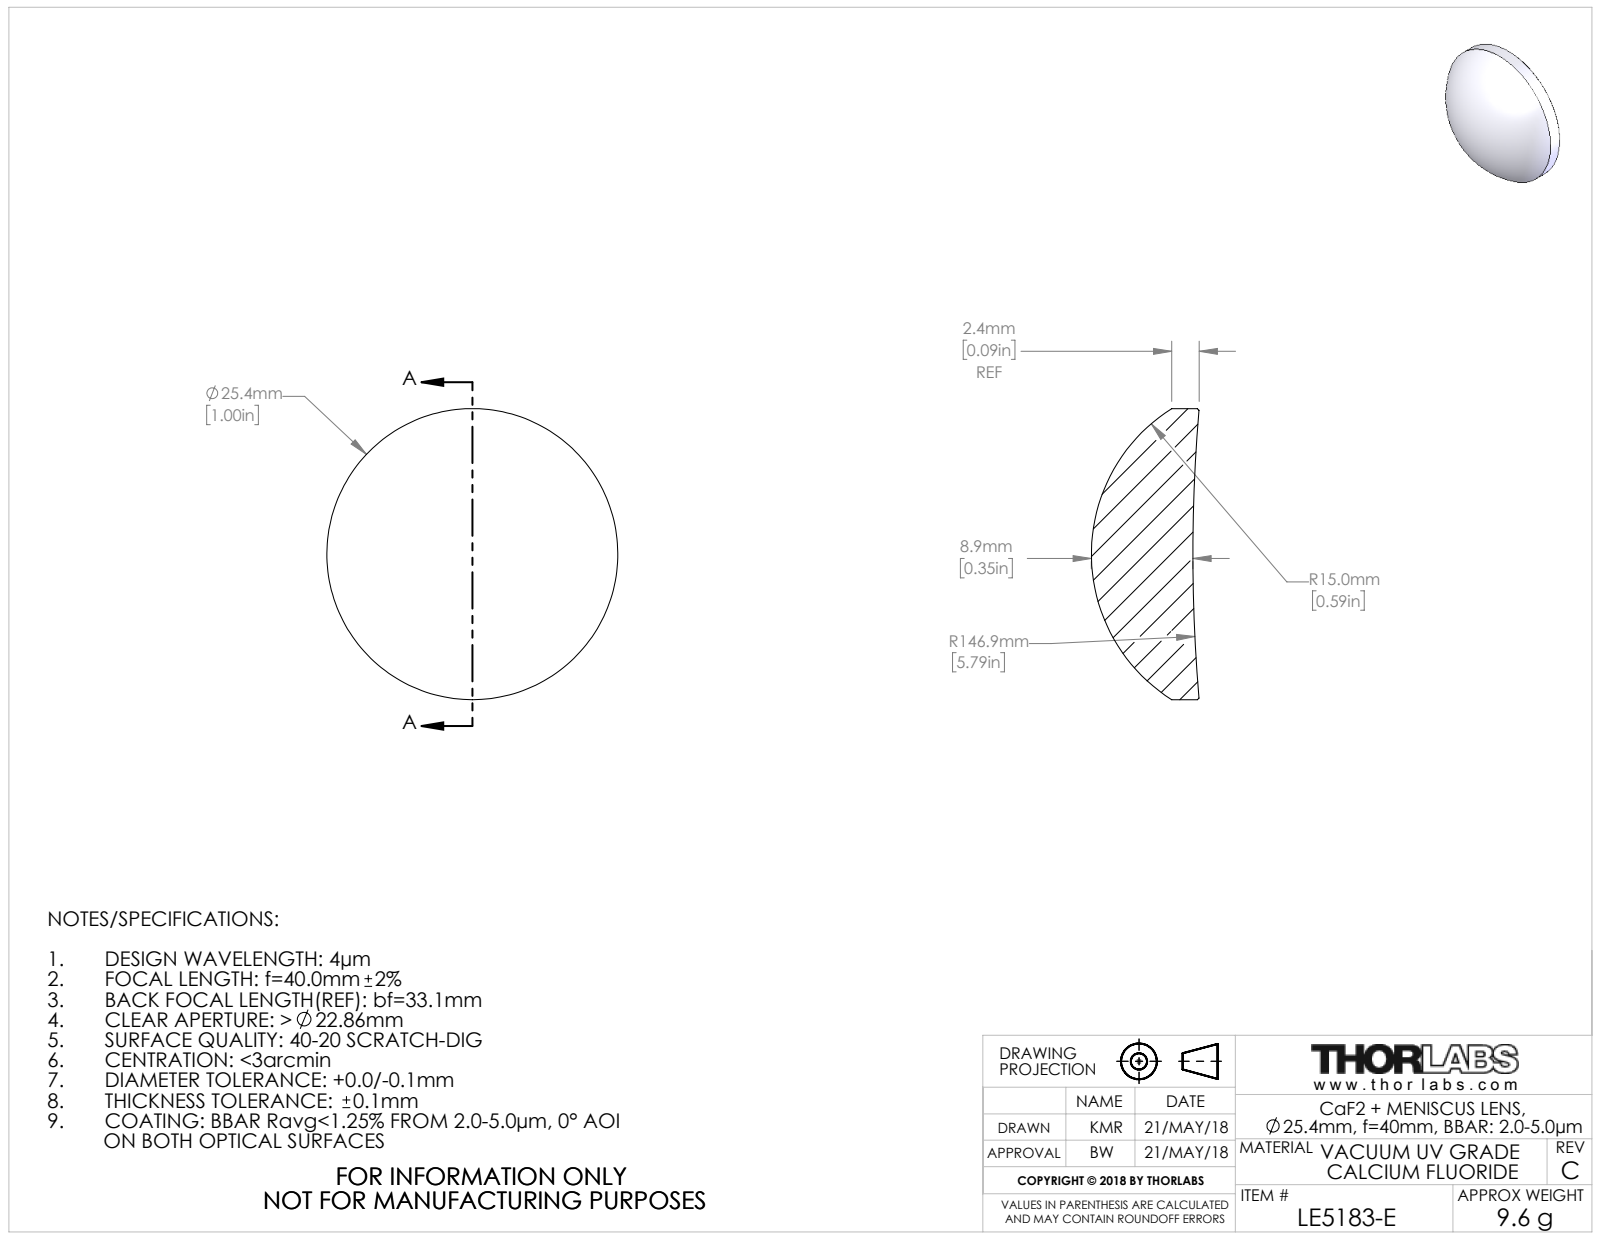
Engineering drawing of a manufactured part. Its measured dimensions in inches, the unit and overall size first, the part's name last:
Units: inches
Overall size (bounding box): 1 × 1 × 0.37
Round bosses / shafts (diameter × count): ⌀1 ×1
Volume: 0.185 in³ · Surface area: 2.096 in²
Bodies: 1 solid, 8 faces (0 planar, 2 cylindrical, 6 other)
Part name (STEP PRODUCT): 20160-E0W
STEP written by: SolidWorks 2016 (CONFIG_CONTROL_DESIGN)
